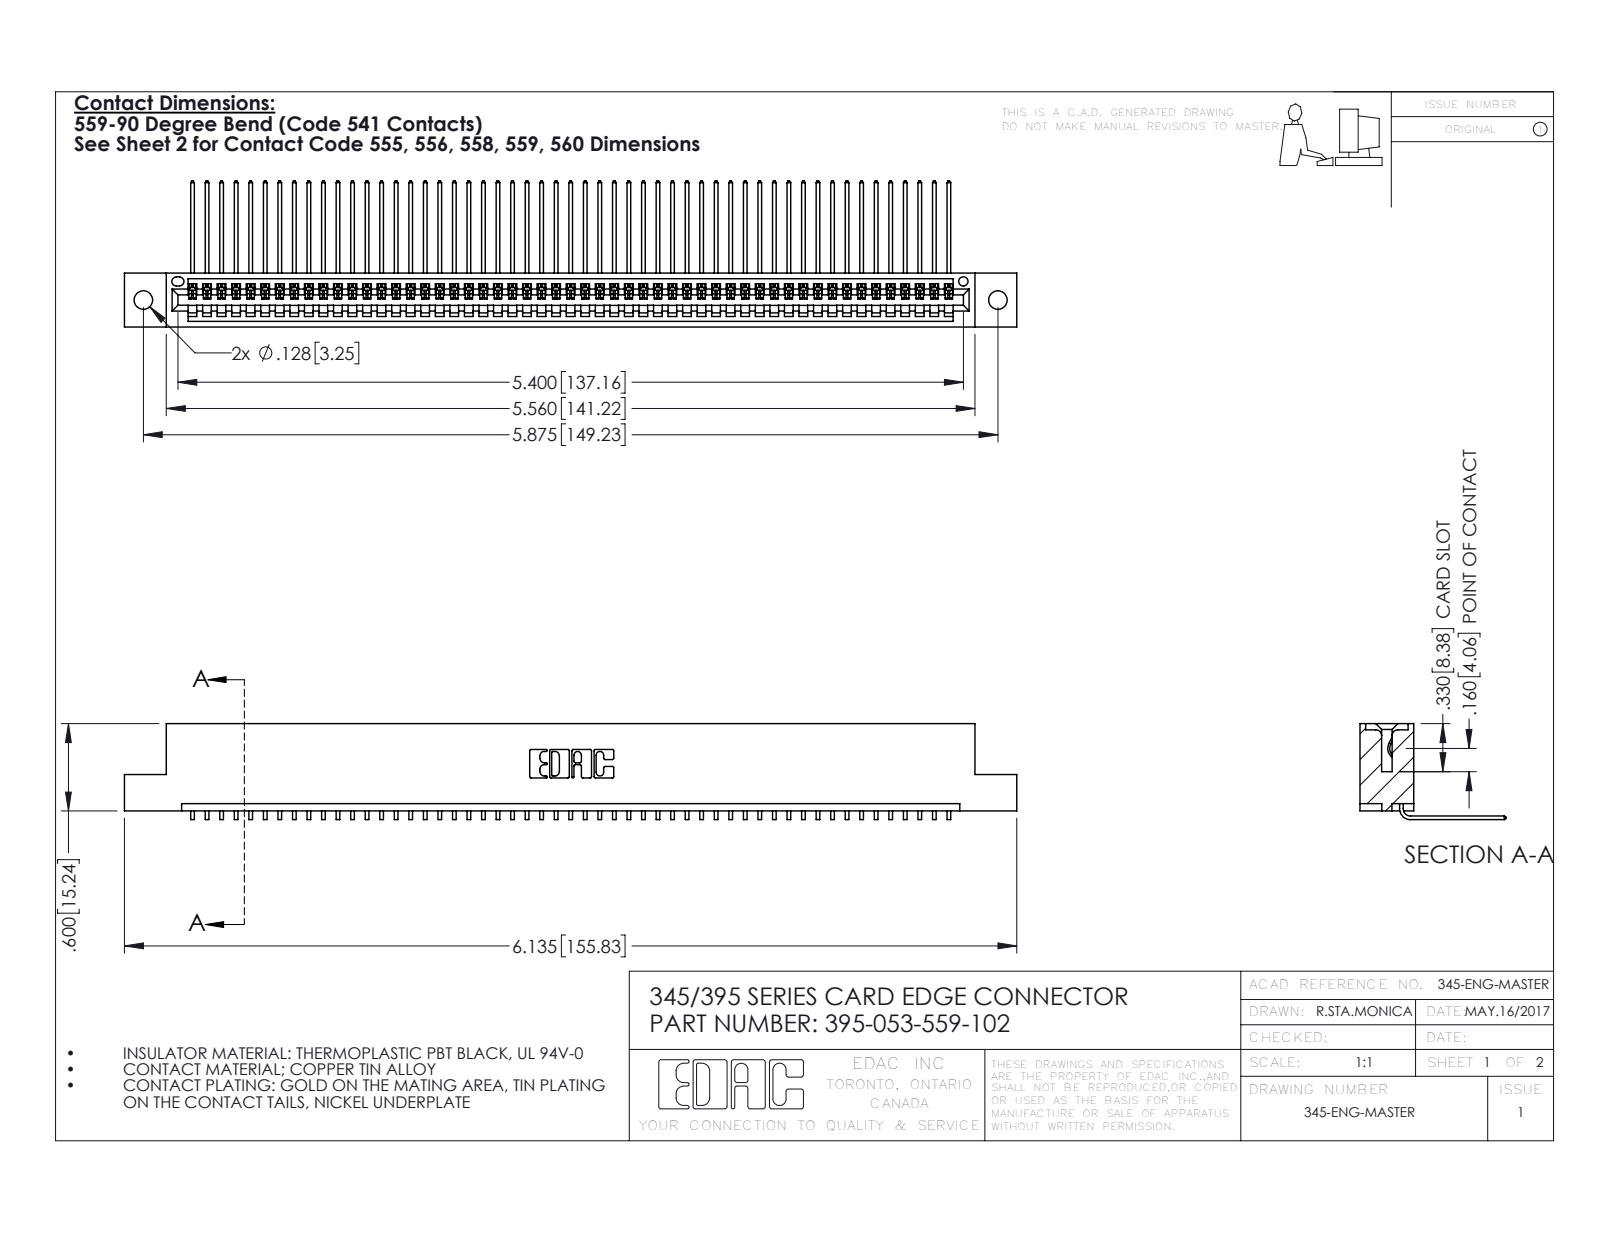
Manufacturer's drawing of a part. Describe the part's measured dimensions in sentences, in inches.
The part is named "345-292-001_558 559 Tail - 1; 395-053-559-102; 345 Part_Flush Mounting Lugs - 0.128 Dia". Its 3-D file was written by "SolidWorks 2016 (CONFIG_CONTROL_DESIGN)". It is 54 solids with 3306 faces: 2306 planar, 1000 cylindrical and 0 other. Overall it measures 6.135 by 1.005 by 0.659 inches. Its volume is 0.917 cubic inches and its surface area 32.38 square inches. Round holes: 2 of diameter 0.128, 1 of diameter 0.064. Partial cylindrical surfaces (rounded edges, fillets, slot ends): 106 of radius 0.006, 22 of radius 0.01, 6 of radius 0.007, 6 of radius 0.031, 3 of radius 0.026, 2 of radius 0.031, 2 of radius 0.04, 1 of radius 0.014. The main face-to-face distances are 0.298, 0.072, 0.37, 0.2, 0.098, 0.272, 0.025, 0.225, 0.149, 0.072. The hole center spacings are 0.27, 5.639, 5.875.
